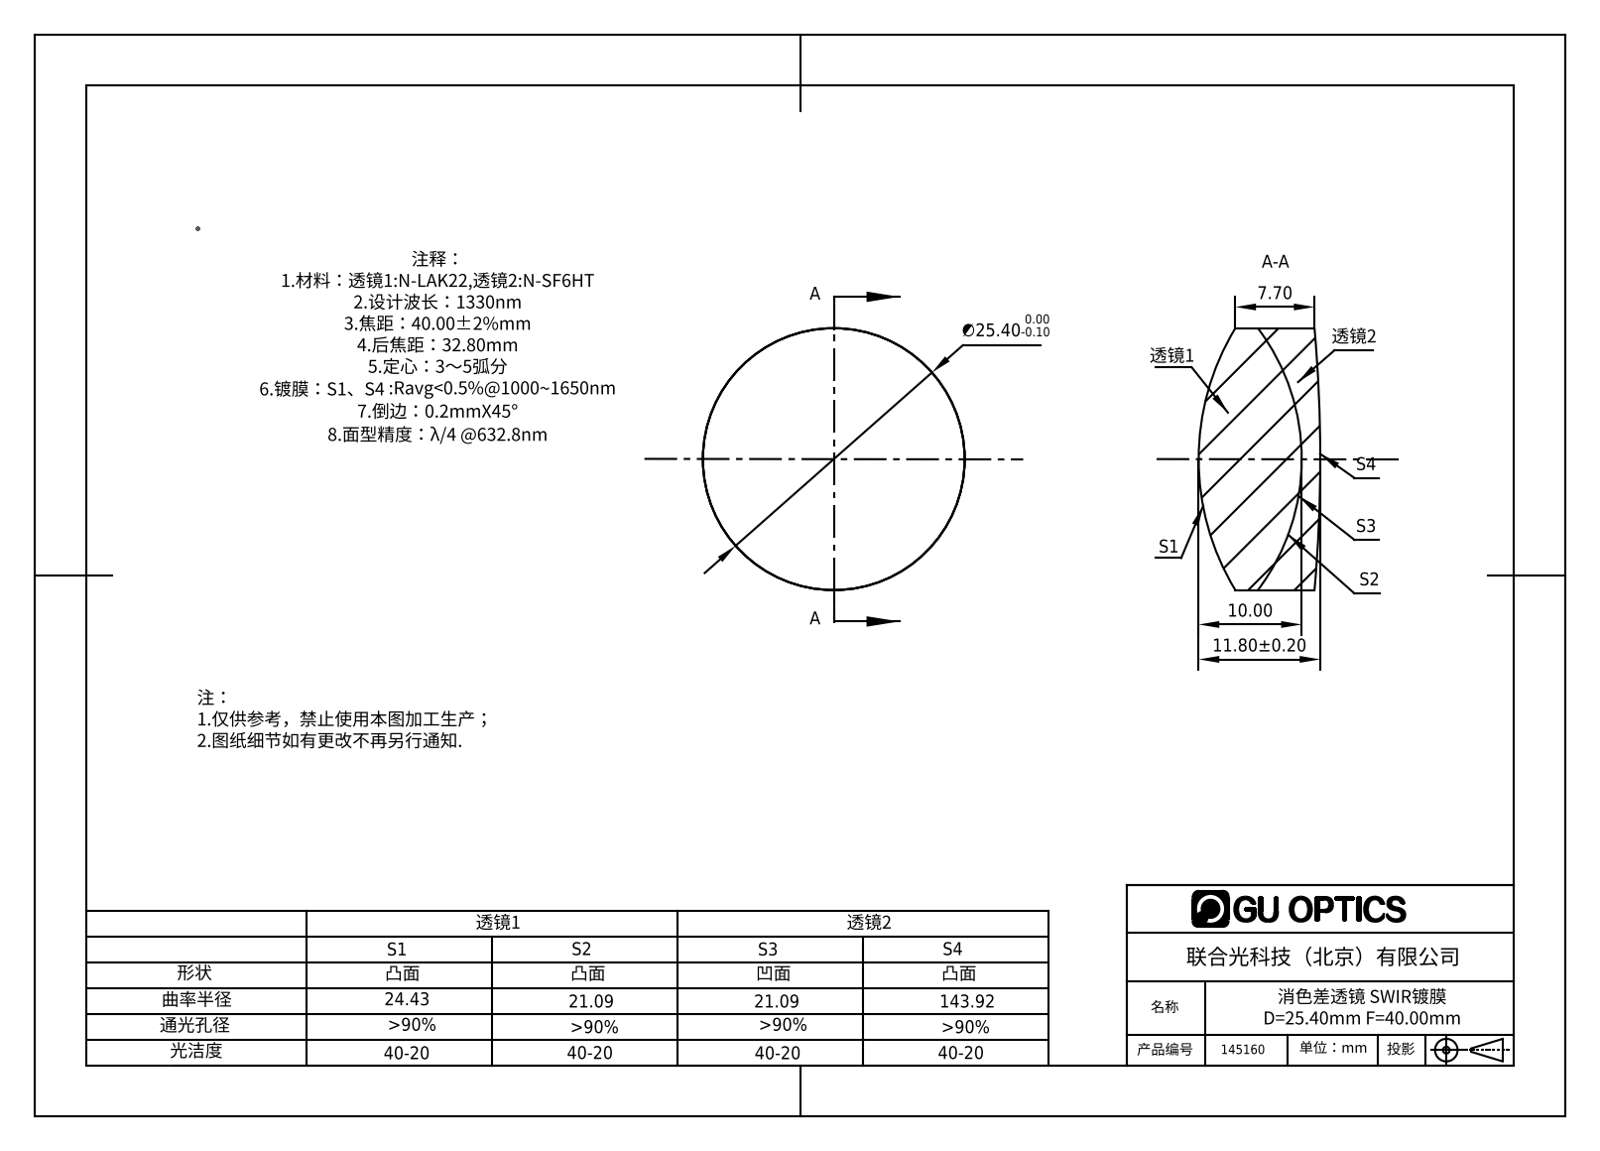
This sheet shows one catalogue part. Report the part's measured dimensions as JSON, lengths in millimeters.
{"part_name": "145160", "step_written_by": "SolidWorks 2016 (AUTOMOTIVE_DESIGN)", "units": "millimeters", "bodies": {"solids": 2, "faces": 12, "planar": 0, "cylindrical": 4, "other": 8}, "overall_size": [25.4, 25.4, 11.8], "volume_mm3": 4959, "surface_area_mm2": 2794, "round_bosses_or_shafts": [[25.4, 1]]}
